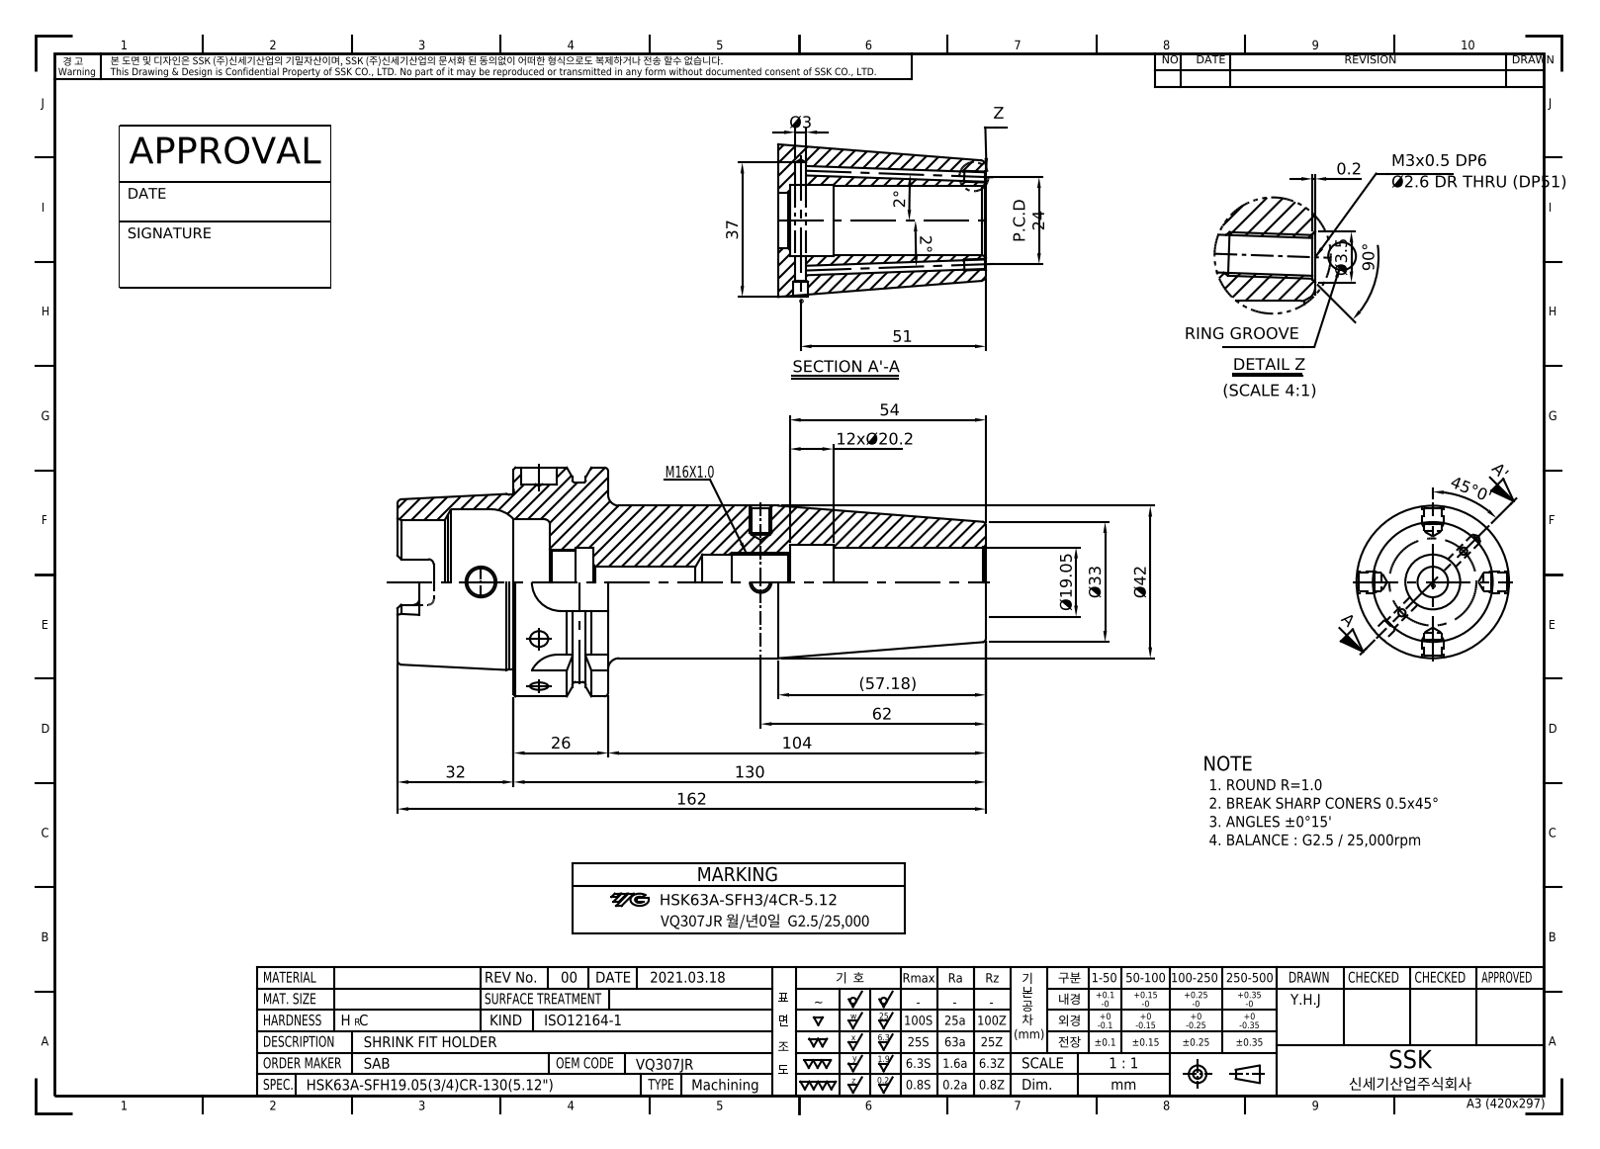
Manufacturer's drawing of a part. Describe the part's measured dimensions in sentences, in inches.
The part is named "LO-HSK63A-SFH19.05CR-130". Its 3-D file was written by "Autodesk Inventor 2022 (AUTOMOTIVE_DESIGN)". It is 1 solid with 121 faces: 42 planar, 36 cylindrical and 43 other. Overall it measures 6.378 by 2.48 by 2.48 inches. Its volume is 11.47 cubic inches and its surface area 62.57 square inches. Round holes: 2 of diameter 0.097, 1 of diameter 0.295, 1 of diameter 0.331, 1 of diameter 0.394, 1 of diameter 0.587, 1 of diameter 0.666, 1 of diameter 0.748, 1 of diameter 0.75, 1 of diameter 0.795, 1 of diameter 1.339, 1 of diameter 1.575. Round bosses or shafts: 1 of diameter 2.48, 1 of diameter 2.165, 1 of diameter 1.891, 1 of diameter 1.654. Partial cylindrical surfaces (rounded edges, fillets, slot ends): 6 of radius 0.059, 4 of radius 0.113, 4 of radius 0.315. The main face-to-face distances are 1.024, 0.394, 0.63, 2.126, 1.26, 4.724, 1.654, 5.118, 4.094, 4.252.
